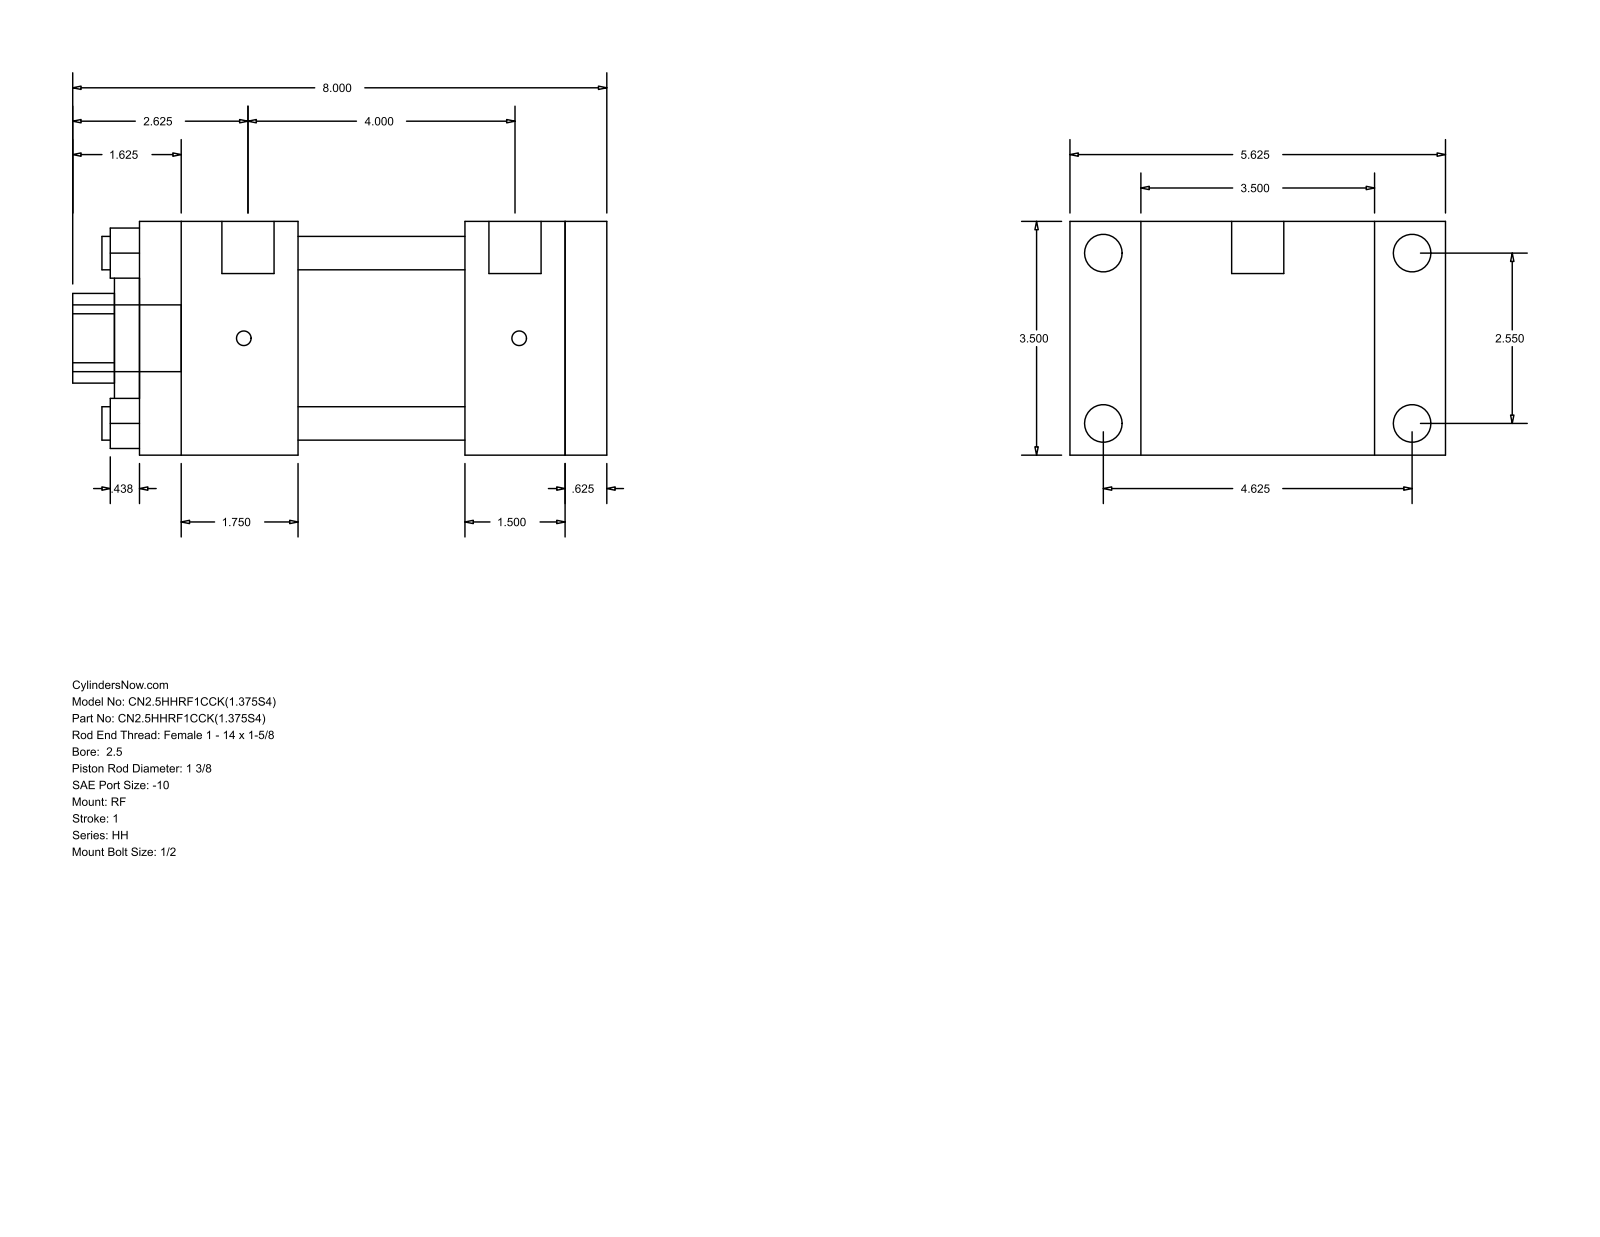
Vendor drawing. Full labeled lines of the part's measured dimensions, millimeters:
Part name (STEP PRODUCT): HH_RF__0250_1.375
STEP written by: GSSL Pune (CONFIG_CONTROL_DESIGN)
Units: millimetres
Bodies: 0 solids, 92 faces (64 planar, 28 cylindrical, 0 other)
Overall size (bounding box): 203.2 × 142.88 × 88.9
Round holes (diameter × count): ⌀12.7 ×4, ⌀34.92 ×1, ⌀50.8 ×1, ⌀73.03 ×1
Round bosses / shafts (diameter × count): ⌀14.3 ×4, ⌀5.56 ×4, ⌀19.84 ×2, ⌀25.4 ×1
Partial cylindrical surfaces — rounded edges, fillets, slot ends (radius × count): R17.06 ×1
Main face-to-face distances: 88.9, 177.8, 15.88, 161.92, 60.32, 101.6, 117.48, 123.82, 63.5, 38.1
Hole centre spacings: 45.79, 64.76, 91.58
